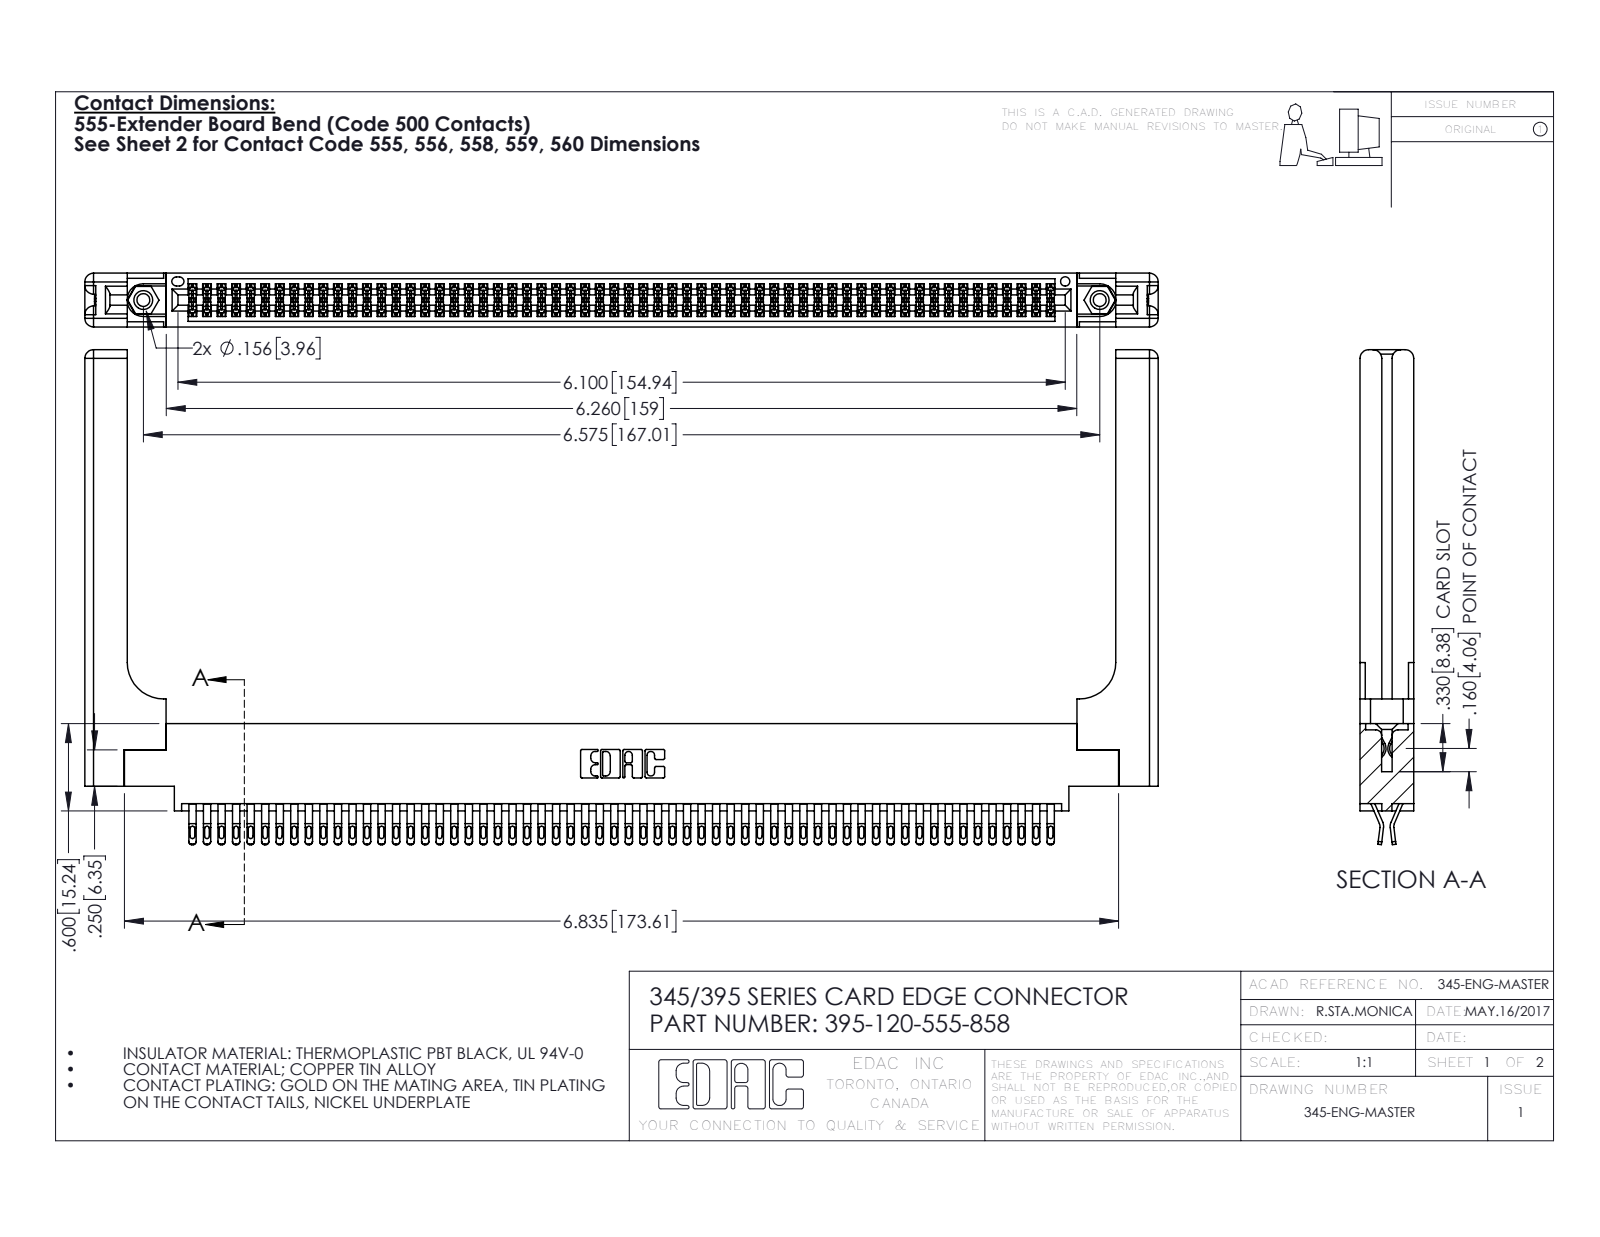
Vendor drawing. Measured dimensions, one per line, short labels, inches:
name: 395-120-555-858; 345-250-001_345-250-001-102; 345-292-001_555 Tail; 345-220-058_345-220-058 (+1 more)
written by: SolidWorks 2016 (CONFIG_CONTROL_DESIGN)
unit: in
bodies: 125 solids, 7106 faces (3952 planar, 3094 cylindrical, 60 other)
size: 7.379 × 3.402 × 0.37
volume: 1.653 in³; area: 53.12 in²
holes: 2× ⌀0.089, 2× ⌀0.125, 2× ⌀0.156, 1× ⌀0.064
bosses: 2× ⌀0.155
rounds: 300× R0.016, 240× R0.02, 180× R0.006, 22× R0.01, 16× R0.06, 6× R0.007, 6× R0.031, 3× R0.026
face distances: 0.072, 0.37, 0.298, 0.025, 0.098, 0.272, 0.2, 0.225, 0.175, 0.148
hole spacings: 0.27, 6.339, 6.575
